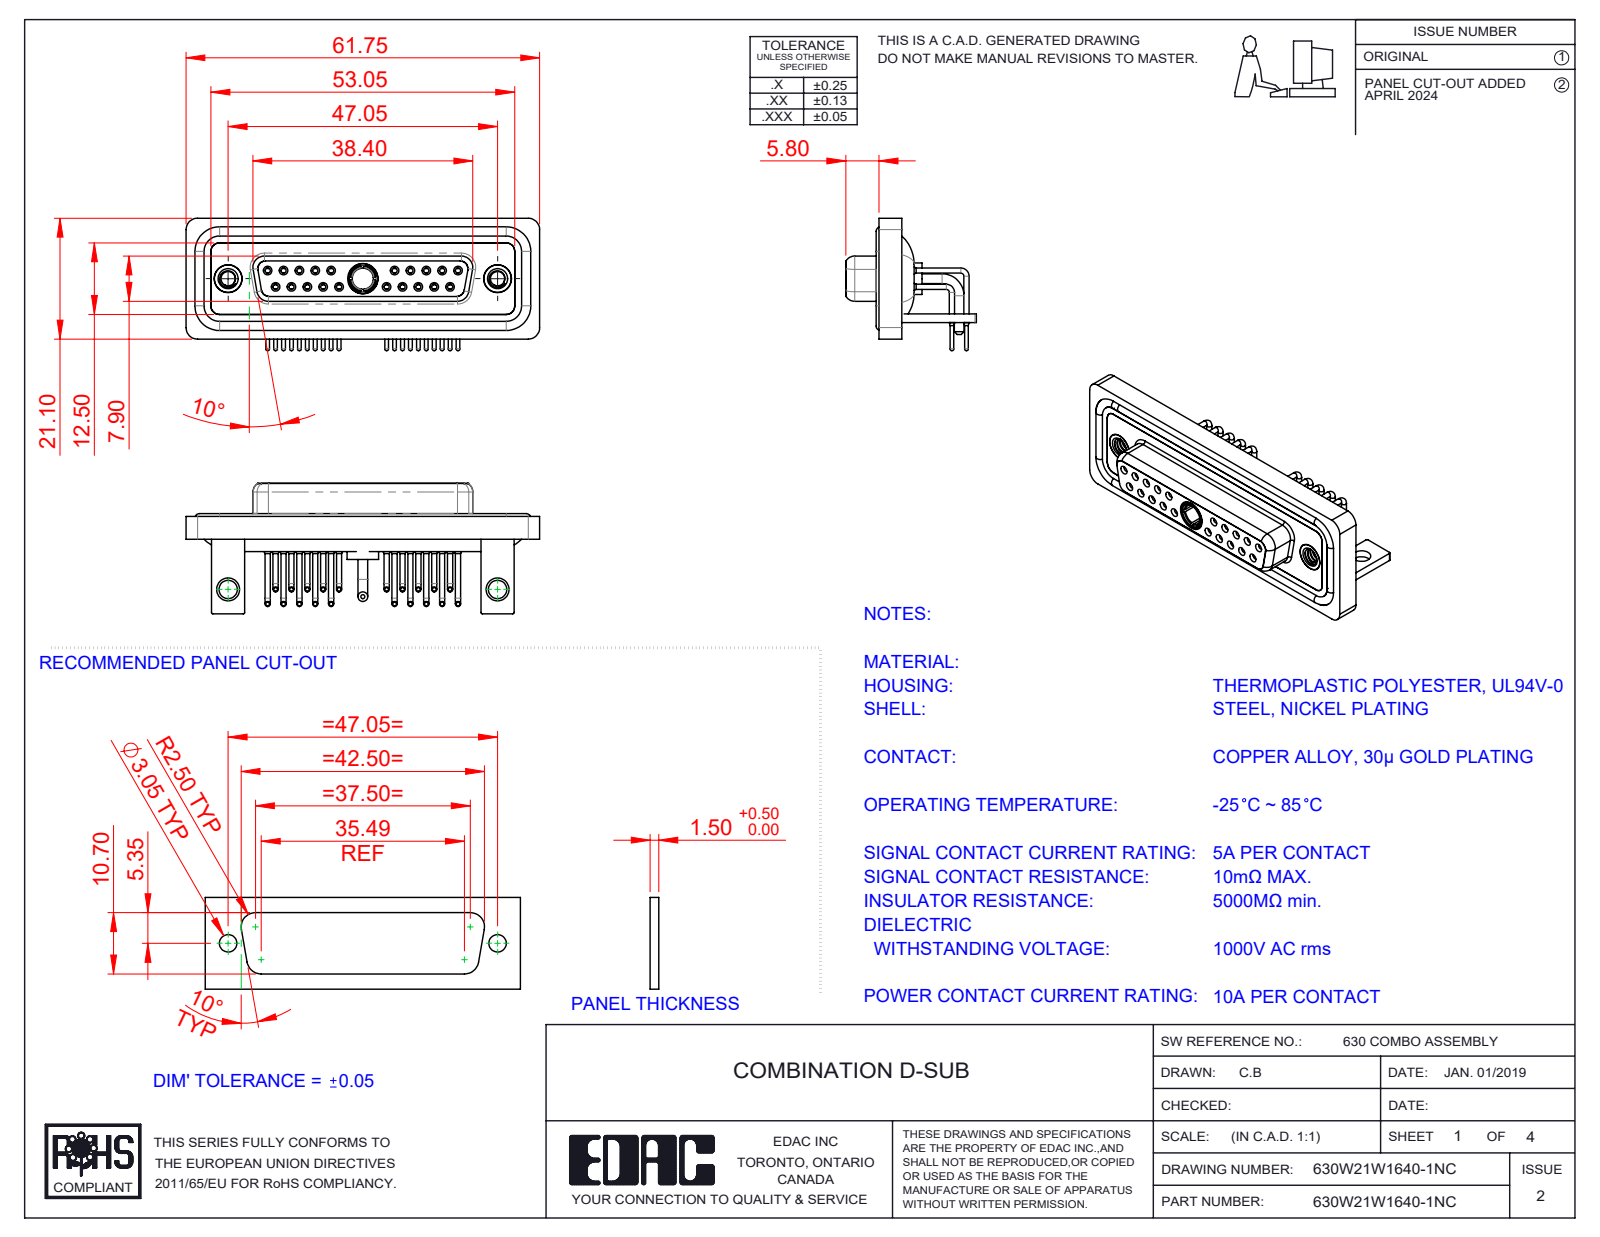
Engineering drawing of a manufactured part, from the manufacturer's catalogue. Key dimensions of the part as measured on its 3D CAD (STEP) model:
Part name (STEP PRODUCT): 630Combo Shell Rear_25 Contacts; 630Combo Stabilizer Bracket_50 Contacts; 630Combo Contact Row 1_50 Contacts; Power Socket_10A RA (+6 more)
STEP written by: SolidWorks 2023 (CONFIG_CONTROL_DESIGN)
Units: millimetres
Bodies: 31 solids, 1566 faces (454 planar, 695 cylindrical, 417 other)
Overall size (bounding box): 61.75 × 23.12 × 22.8
Volume: 8 807 mm³ · Surface area: 15 468 mm²
Round holes (diameter × count): ⌀0.9 ×20, ⌀1.1 ×20, ⌀1.5 ×20, ⌀2 ×20, ⌀1.6 ×10, ⌀1.7 ×10, ⌀4.85 ×3, ⌀2.5 ×2, ⌀3.2 ×2, ⌀4 ×2, ⌀4.05 ×2, ⌀5 ×2
Round bosses / shafts (diameter × count): ⌀0.9 ×20, ⌀0.65 ×20, ⌀1.6 ×14, ⌀4.95 ×2, ⌀4.8 ×2, ⌀1.7 ×2, ⌀5.5 ×1, ⌀5.2 ×1
Partial cylindrical surfaces — rounded edges, fillets, slot ends (radius × count): R2 ×19, R1.5 ×18, R0.25 ×16, R1.35 ×8, R1.6 ×8, R0.5 ×5, R0.6 ×4, R0.65 ×4
Main face-to-face distances: 0.4, 1.8, 2.9, 3.7, 1.5, 4.1, 1.1, 1.4, 1.6, 2.5
Hole centre spacings: 3.16, 2.77, 5.54, 8.31, 5.04, 19.39, 20.97, 22.16
